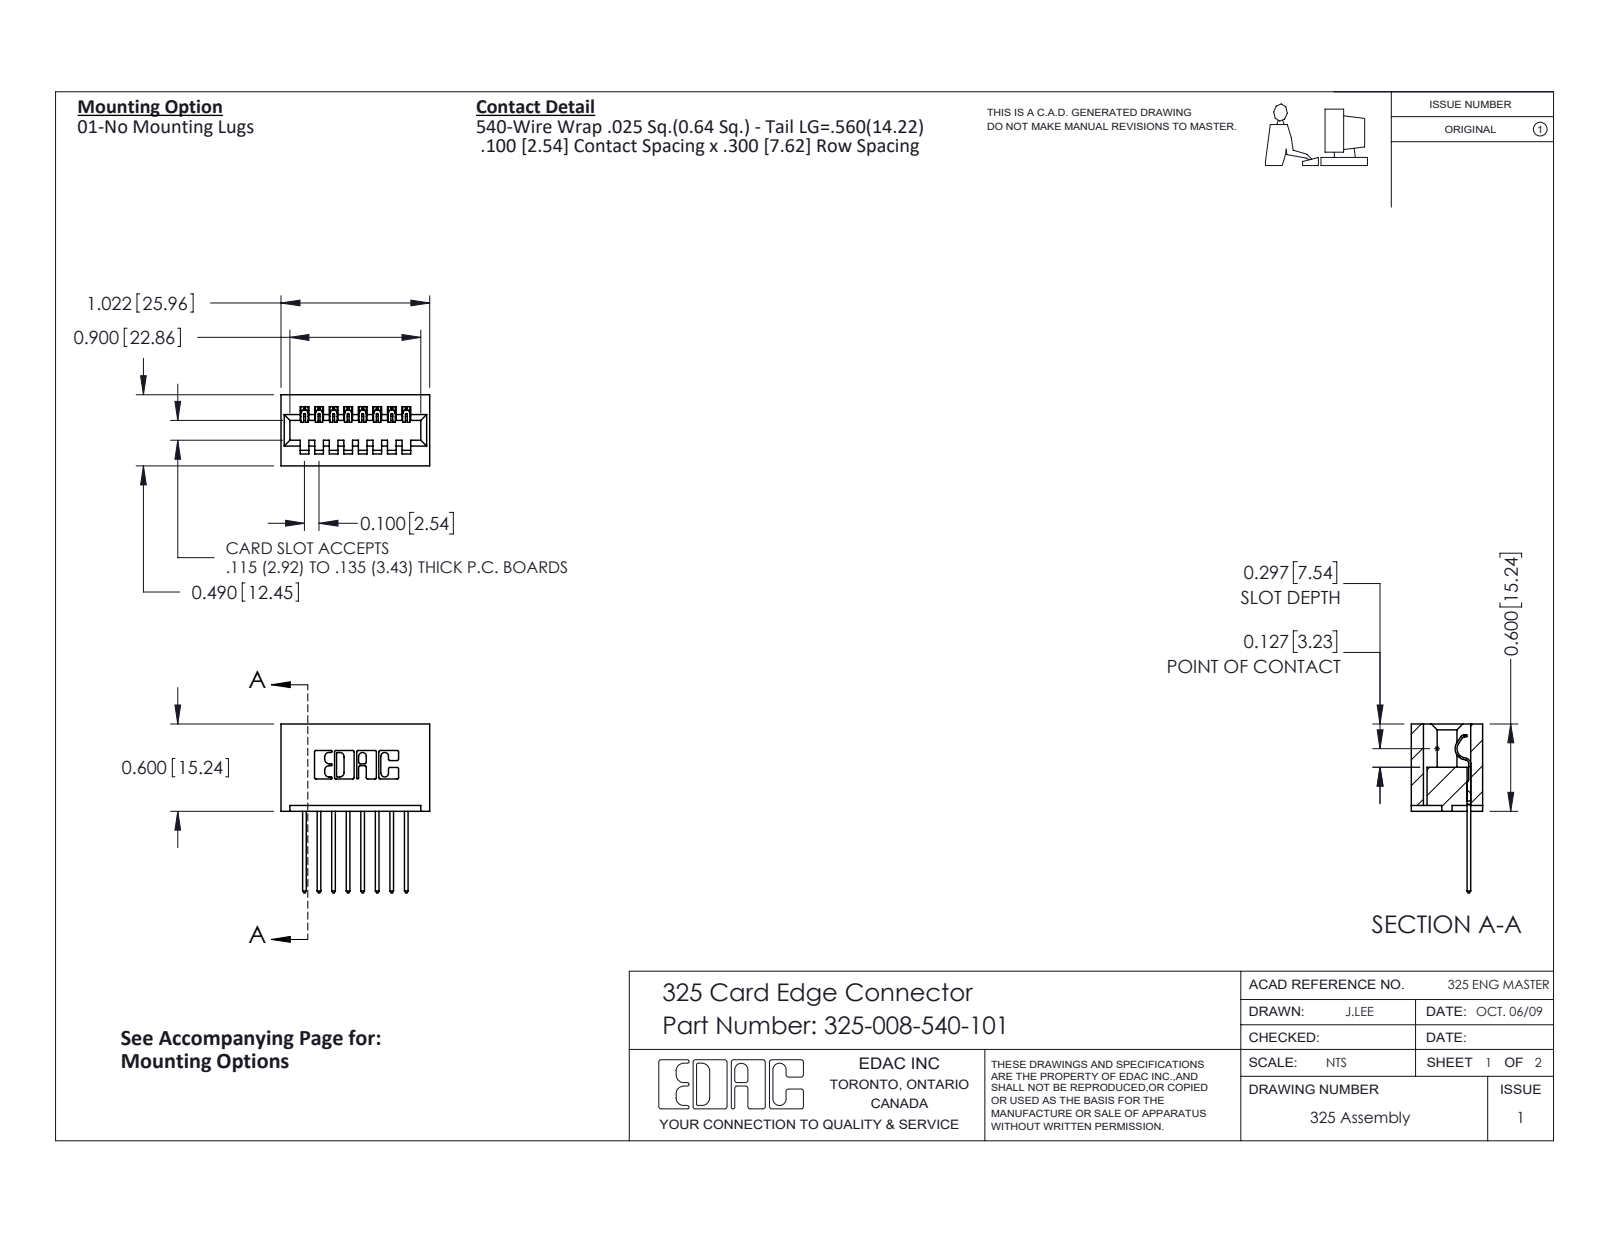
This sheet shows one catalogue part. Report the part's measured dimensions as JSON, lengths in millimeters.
{"part_name": "325-292-001_325-293-140; 325 Part_Lugless; 325-008-540-101", "step_written_by": "SolidWorks 2016 (CONFIG_CONTROL_DESIGN)", "units": "millimeters", "bodies": {"solids": 9, "faces": 570, "planar": 402, "cylindrical": 168, "other": 0}, "overall_size": [29.5, 26, 12.4], "volume_mm3": 3610, "surface_area_mm2": 3938, "partial_cylinders_radius": [[0.3, 22], [0.2, 16], [0.3, 16], [0.2, 6], [0.8, 6], [0.7, 3], [0.4, 1], [0.6, 1]], "face_to_face_distances": [7.6, 2.5, 5.1, 2.1, 10.3, 1, 10.2, 1.5, 12.4, 4.1]}
